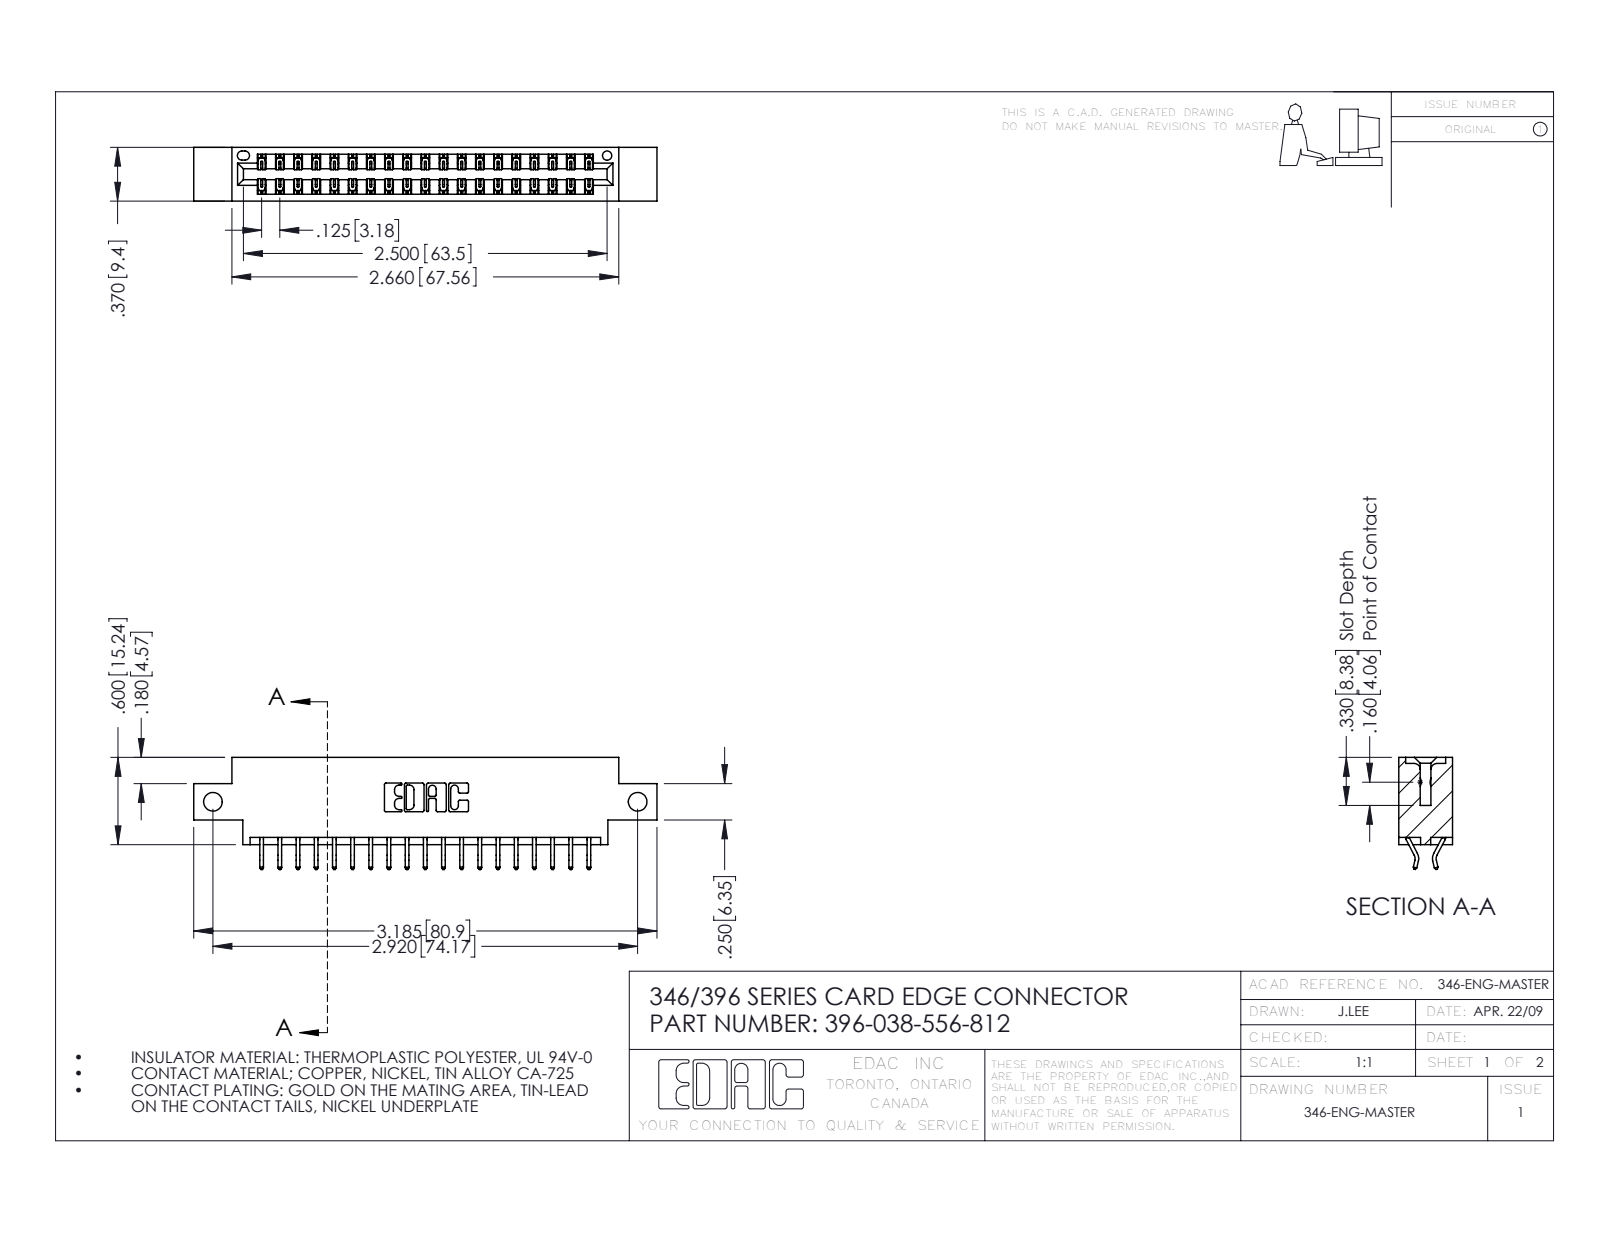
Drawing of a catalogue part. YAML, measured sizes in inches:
part_name: "345-292-001_556 Tail; 346 Part_0.170 Offset - Side Mount; 396-038-556-812"
step_written_by: "SolidWorks 2016 (CONFIG_CONTROL_DESIGN)"
units: inches
bodies: {solids: 39, faces: 2330, planar: 1562, cylindrical: 768, other: 0}
overall_size: [3.185, 0.77, 0.37]
volume: 0.456
surface_area: 15.36
round_holes:
  - {diameter: 0.128, count: 2}
  - {diameter: 0.064, count: 1}
partial_cylinders:
  - {radius: 0.006, count: 57}
  - {radius: 0.01, count: 22}
  - {radius: 0.007, count: 6}
  - {radius: 0.031, count: 6}
  - {radius: 0.026, count: 3}
  - {radius: 0.01, count: 2}
  - {radius: 0.014, count: 2}
  - {radius: 0.022, count: 2}
face_to_face_distances: [0.048, 0.322, 0.37, 0.25, 0.025, 0.072, 0.298, 0.275, 0.148, 0.222]
hole_center_spacings: [2.92]
